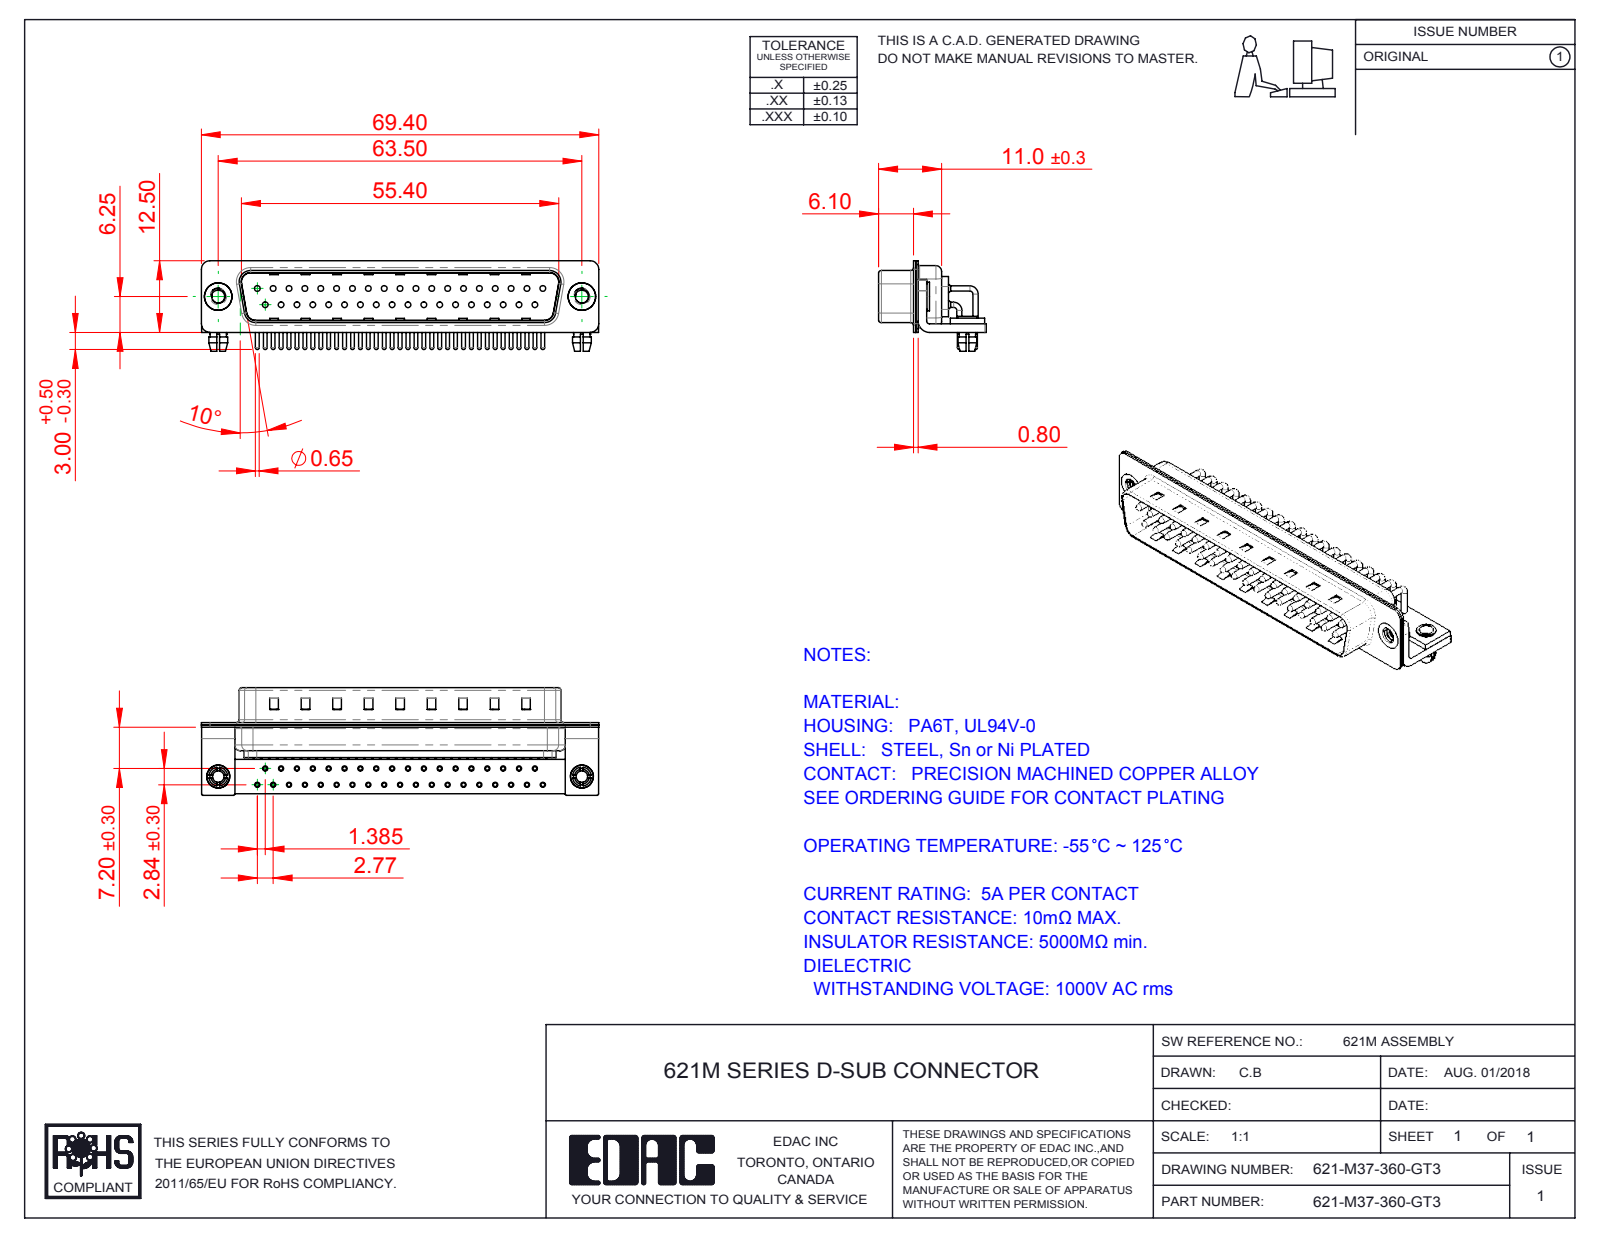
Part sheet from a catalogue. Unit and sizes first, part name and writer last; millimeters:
Units: millimetres
Overall size (bounding box): 69.4 × 18.8 × 15.8
Round holes (diameter × count): ⌀2 ×39, ⌀0.9 ×37, ⌀1 ×37, ⌀1.7 ×37, ⌀2.26 ×2, ⌀2.5 ×2, ⌀3.2 ×2, ⌀4 ×2, ⌀4.8 ×2
Round bosses / shafts (diameter × count): ⌀0.9 ×46, ⌀1.5 ×37, ⌀0.65 ×37, ⌀5 ×2, ⌀4.9 ×2, ⌀4 ×2, ⌀3.4 ×2, ⌀3.3 ×2
Partial cylindrical surfaces — rounded edges, fillets, slot ends (radius × count): R1.01 ×37, R0.25 ×16, R1.5 ×16, R2 ×13, R0.5 ×9, R1.6 ×8, R0.6 ×4, R0.65 ×4
Main face-to-face distances: 0.4, 0.85, 1.25, 9.55, 1.5, 10.4, 8.3, 0.8, 8.7, 1
Hole centre spacings: 3.16, 2.77, 5.54, 8.31, 11.08, 13.85, 5.03, 16.62
Volume: 4 643 mm³ · Surface area: 12 155 mm²
Bodies: 47 solids, 4698 faces (2645 planar, 1601 cylindrical, 452 other)
Part name (STEP PRODUCT): 621M Stabilizer Board_37 Contacts; 621M Board Lock; 621M 4-40 Threaded Rivet_Stabilizer; 621M Stabilizer Bracket (+6 more)
STEP written by: SolidWorks 2016 (CONFIG_CONTROL_DESIGN)
